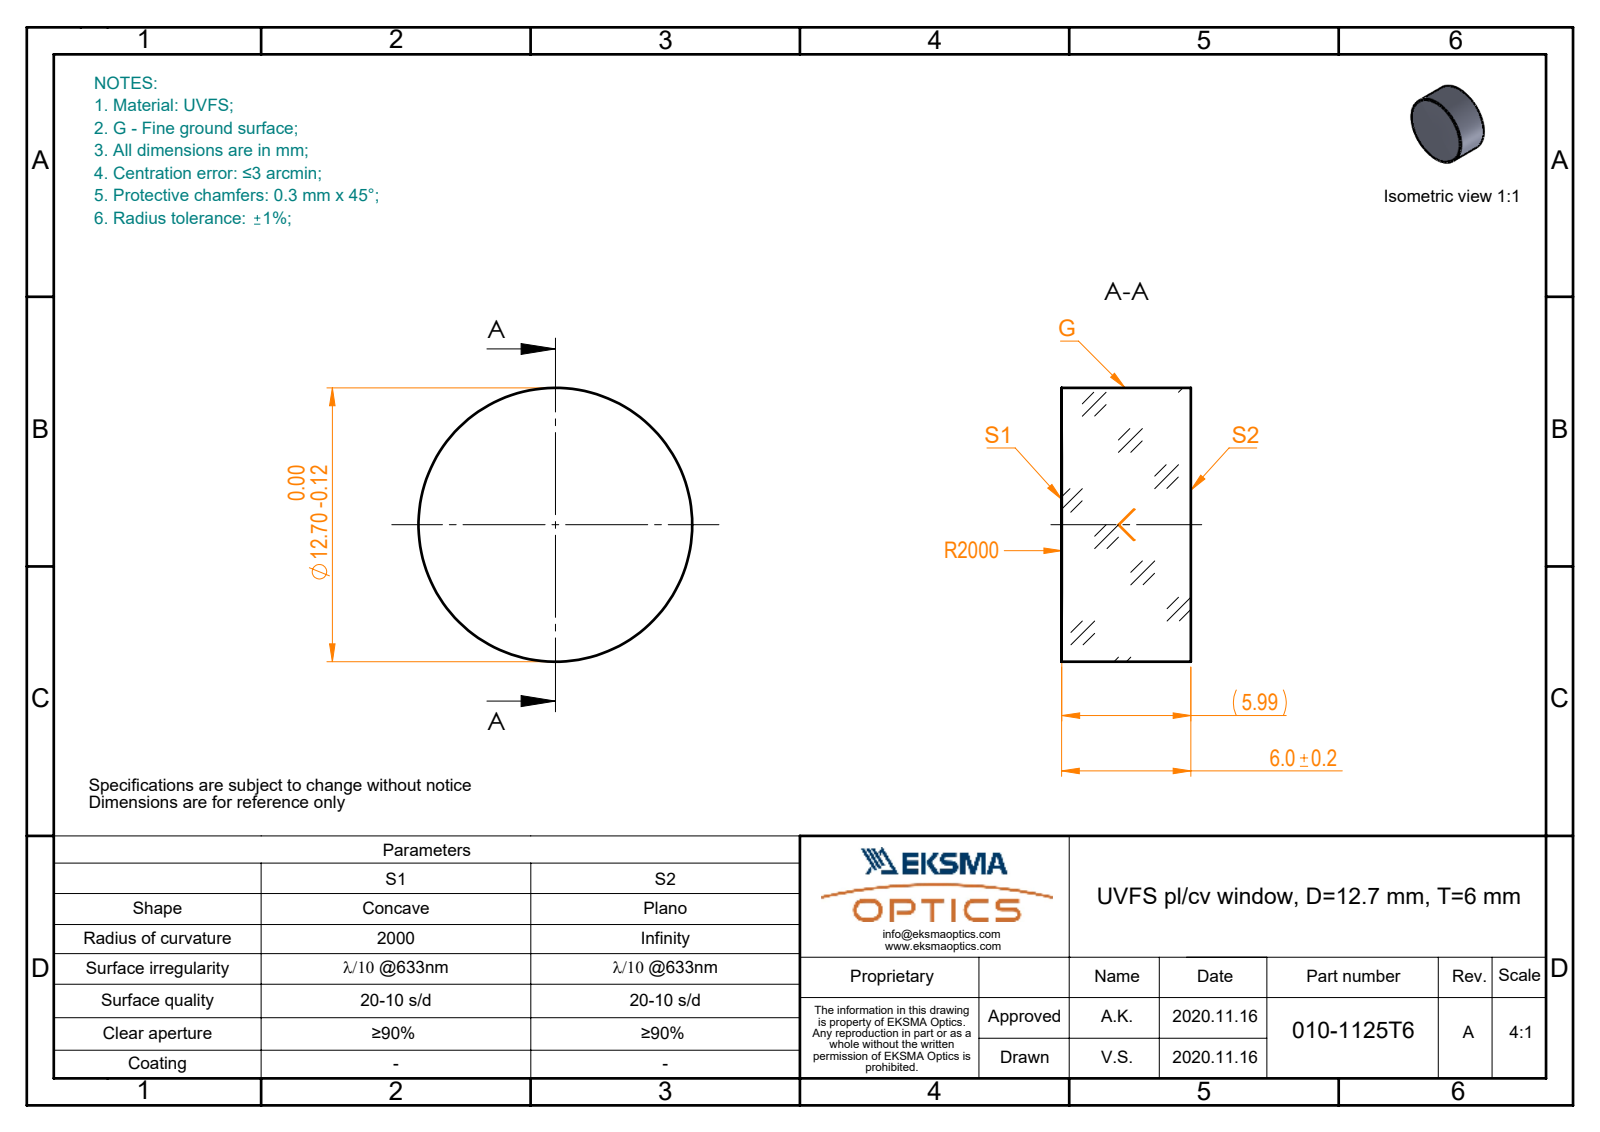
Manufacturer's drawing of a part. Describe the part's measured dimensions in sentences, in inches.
The part is named "010-1125T6_UVFS_PCV_window". Its 3-D file was written by "SolidWorks 2019 (CONFIG_CONTROL_DESIGN)". It is 1 solid with 5 faces: 1 planar, 2 cylindrical and 2 other. Overall it measures 0.5 by 0.5 by 0.236 inches. Its volume is 0.046 cubic inches and its surface area 0.764 square inches. Round bosses or shafts: 1 of diameter 0.5.
